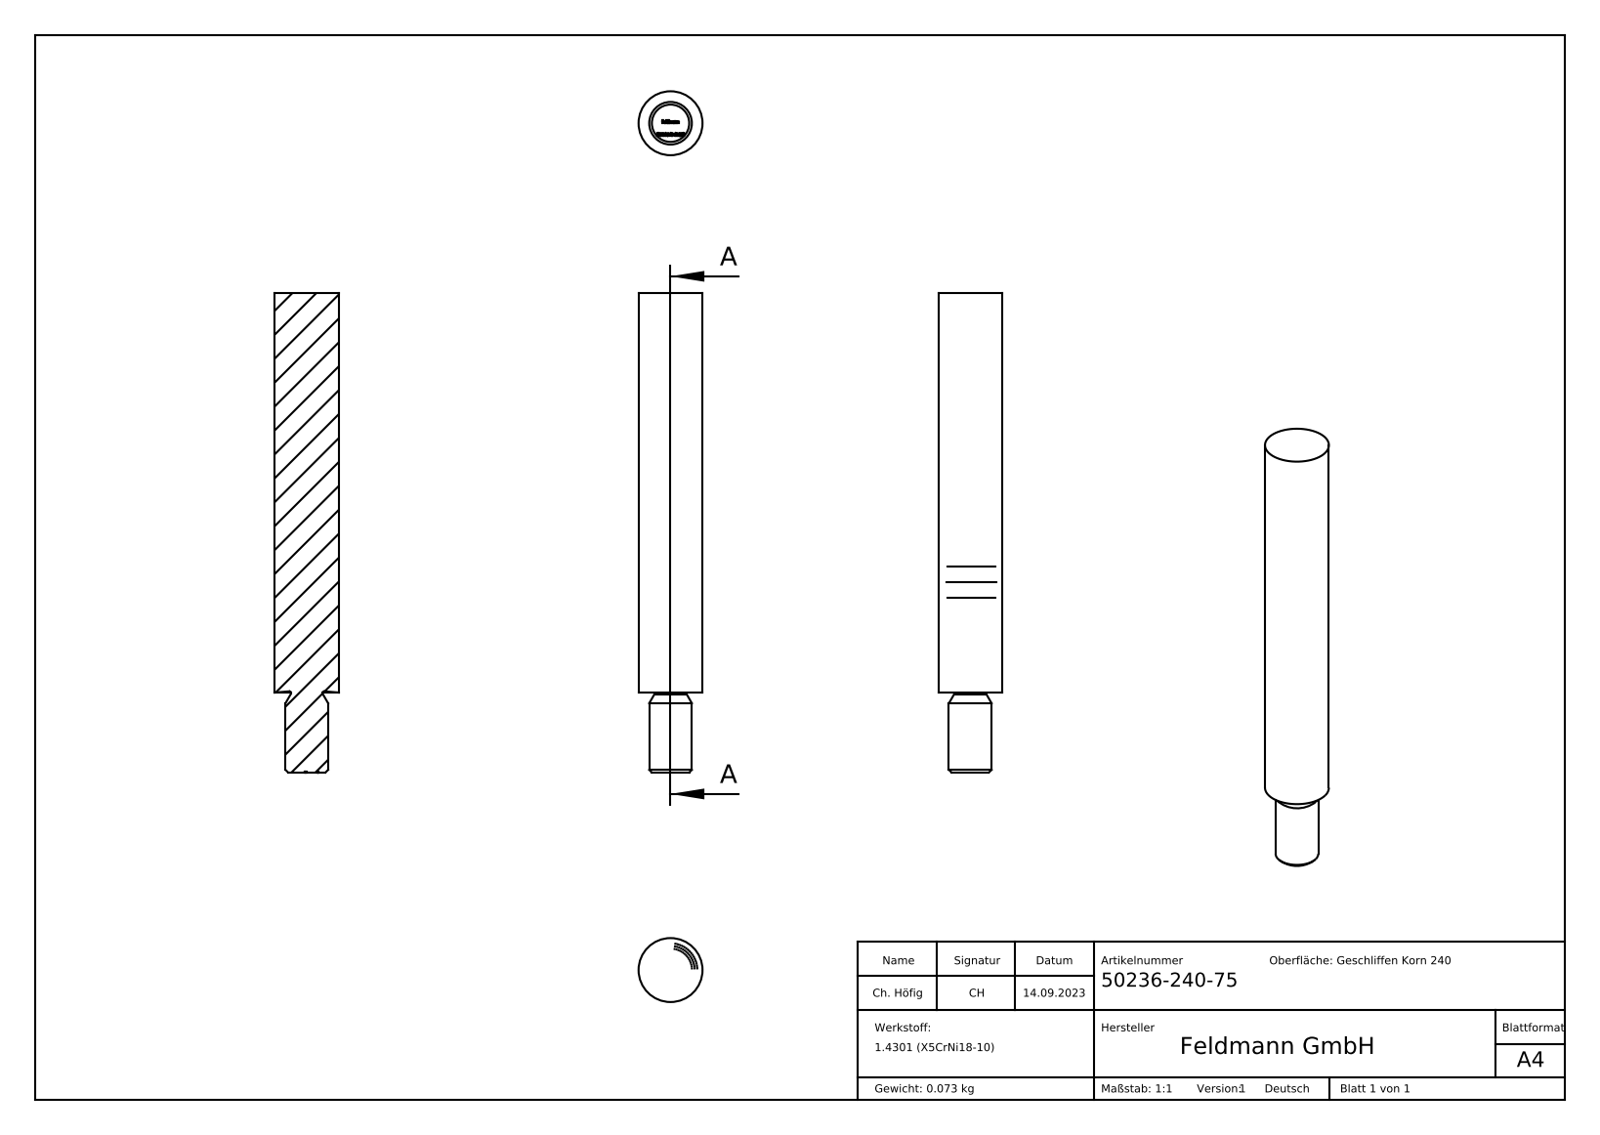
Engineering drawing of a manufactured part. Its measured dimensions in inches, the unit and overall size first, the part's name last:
Units: inches
Overall size (bounding box): 3.543 × 0.472 × 0.472
Round bosses / shafts (diameter × count): ⌀0.472 ×1, ⌀0.315 ×1
Main face-to-face distances: 3.543, 3.539, 0.03, 0.051, 0.094, 0.094, 0.028, 0.061, 0.096, 0.022
Volume: 0.561 in³ · Surface area: 5.349 in²
Bodies: 1 solid, 266 faces (157 planar, 2 cylindrical, 107 other)
Part name (STEP PRODUCT): 50236-240-75
STEP written by: SolidWorks 2018 (CONFIG_CONTROL_DESIGN)
